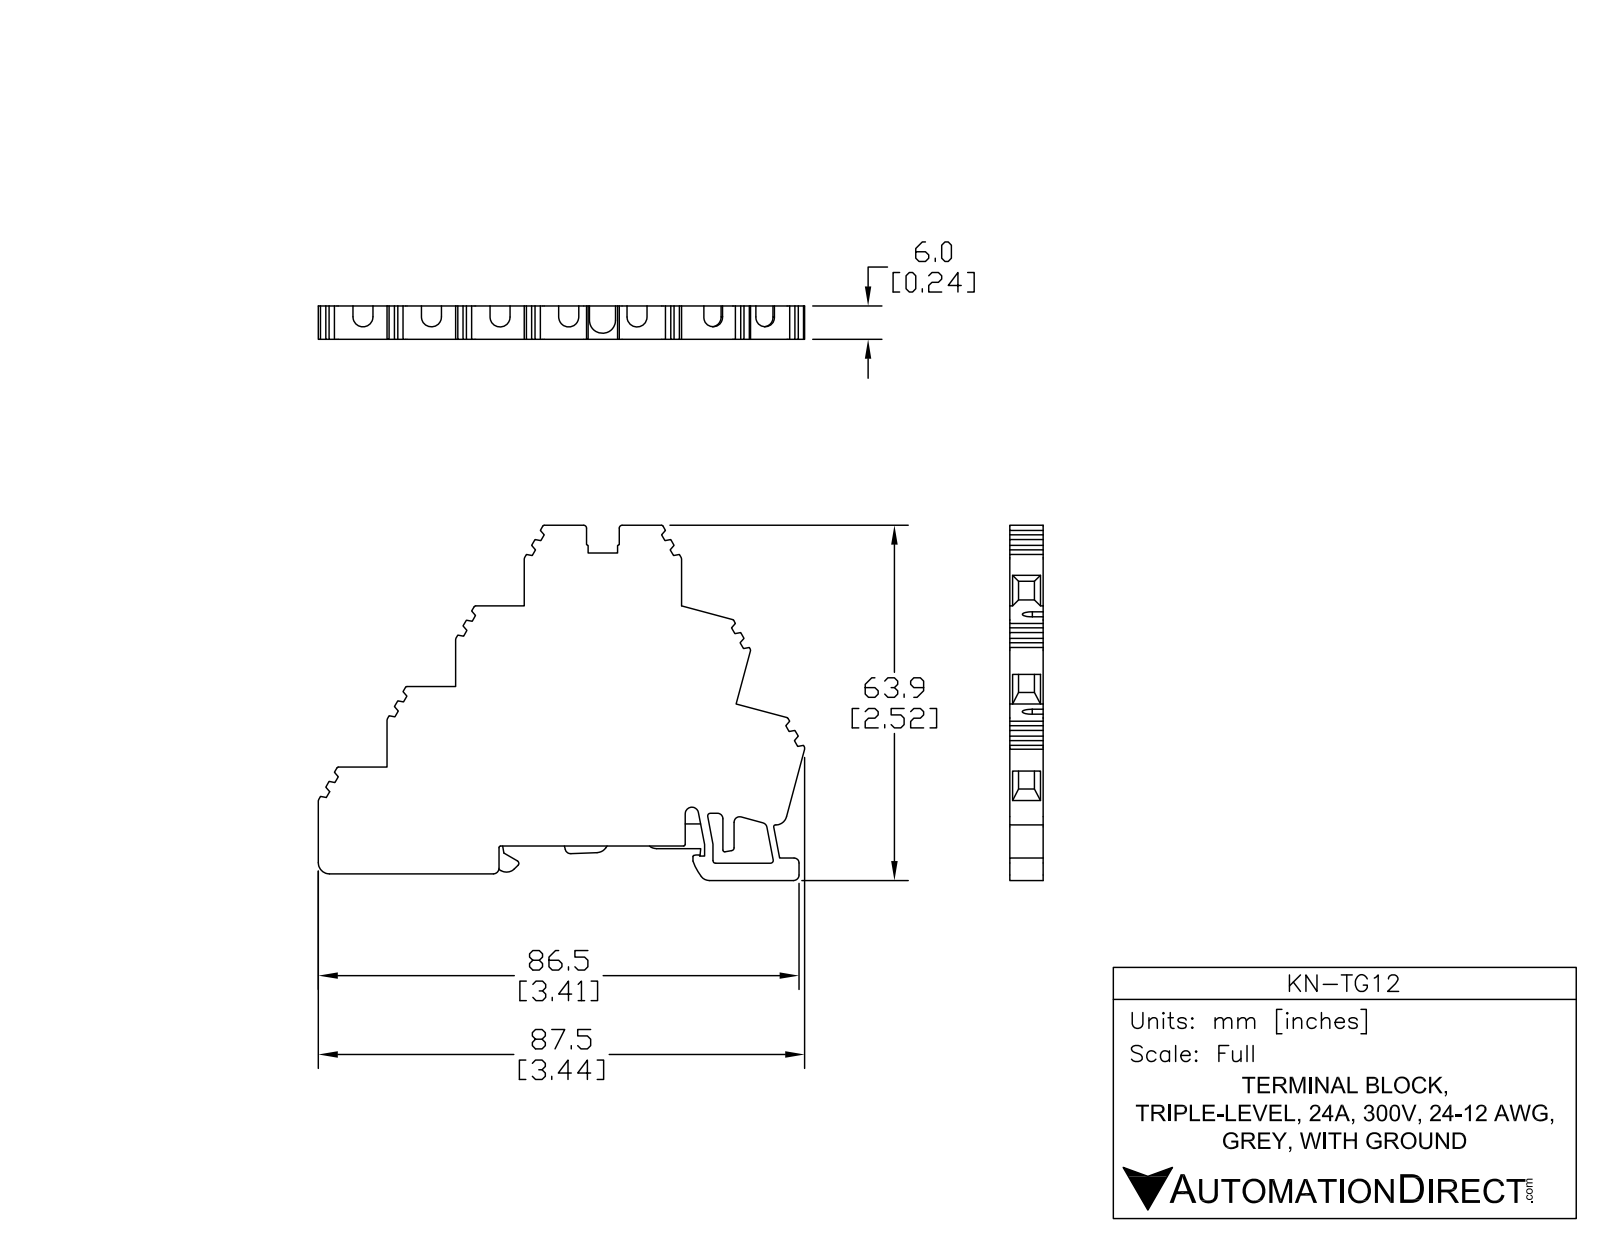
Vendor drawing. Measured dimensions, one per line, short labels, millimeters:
name: KN-TG12
written by: SolidWorks 2014 (AUTOMOTIVE_DESIGN)
unit: mm
bodies: 2 solids, 252 faces (189 planar, 63 cylindrical, 0 other)
size: 87.5 × 63.9 × 6
volume: 20 494 mm³; area: 10 253 mm²
rounds: 14× R0.3, 13× R0.5, 6× R1, 6× R1.8, 5× R2, 1× R0.2, 1× R0.9, 1× R1.2
face distances: 6, 1.75, 4.25, 2.5, 14.5, 5, 1, 1.2, 3.1, 29
